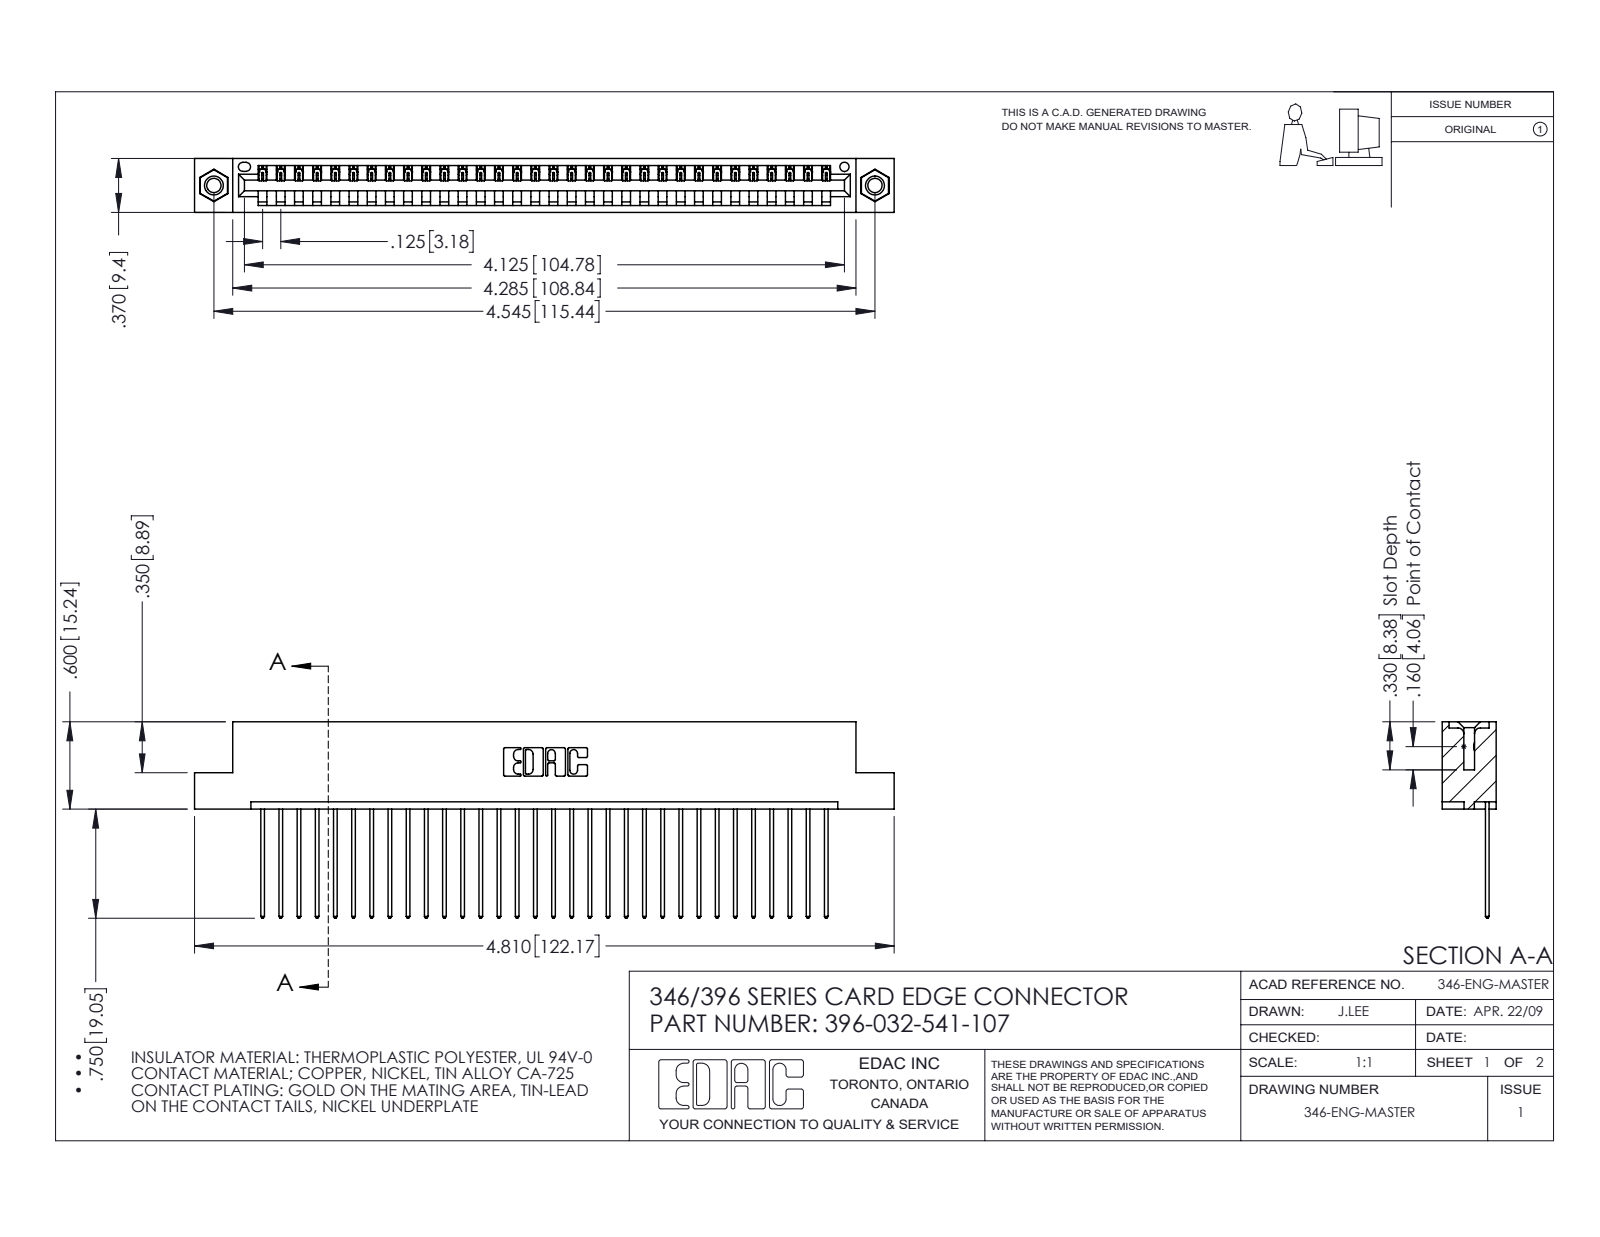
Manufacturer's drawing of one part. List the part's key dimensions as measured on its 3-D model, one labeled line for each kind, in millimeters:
Part name (STEP PRODUCT): 345-250-001_345-250-005-103; 396-032-541-107; 345-292-001_345-293-141; 346 Part_Flush Mounting Lugs - 0.156 Dia-TI
STEP written by: SolidWorks 2016 (CONFIG_CONTROL_DESIGN)
Units: millimetres
Bodies: 35 solids, 2038 faces (1388 planar, 634 cylindrical, 16 other)
Overall size (bounding box): 122.2 × 34.3 × 9.4
Volume: 11 700 mm³ · Surface area: 15 210 mm²
Round holes (diameter × count): ⌀2.5 ×2, ⌀3.2 ×2, ⌀4 ×2, ⌀1.6 ×1
Round bosses / shafts (diameter × count): ⌀3.9 ×2
Partial cylindrical surfaces — rounded edges, fillets, slot ends (radius × count): R0.2 ×64, R0.3 ×64, R0.3 ×22, R0.2 ×6, R0.8 ×6, R0.7 ×3, R0.8 ×2, R1 ×2
Main face-to-face distances: 1.2, 8.2, 9.4, 6.4, 1.8, 7.6, 0.6, 3.8, 5.6, 2.5
Hole centre spacings: 6.2, 110.2, 115.4
